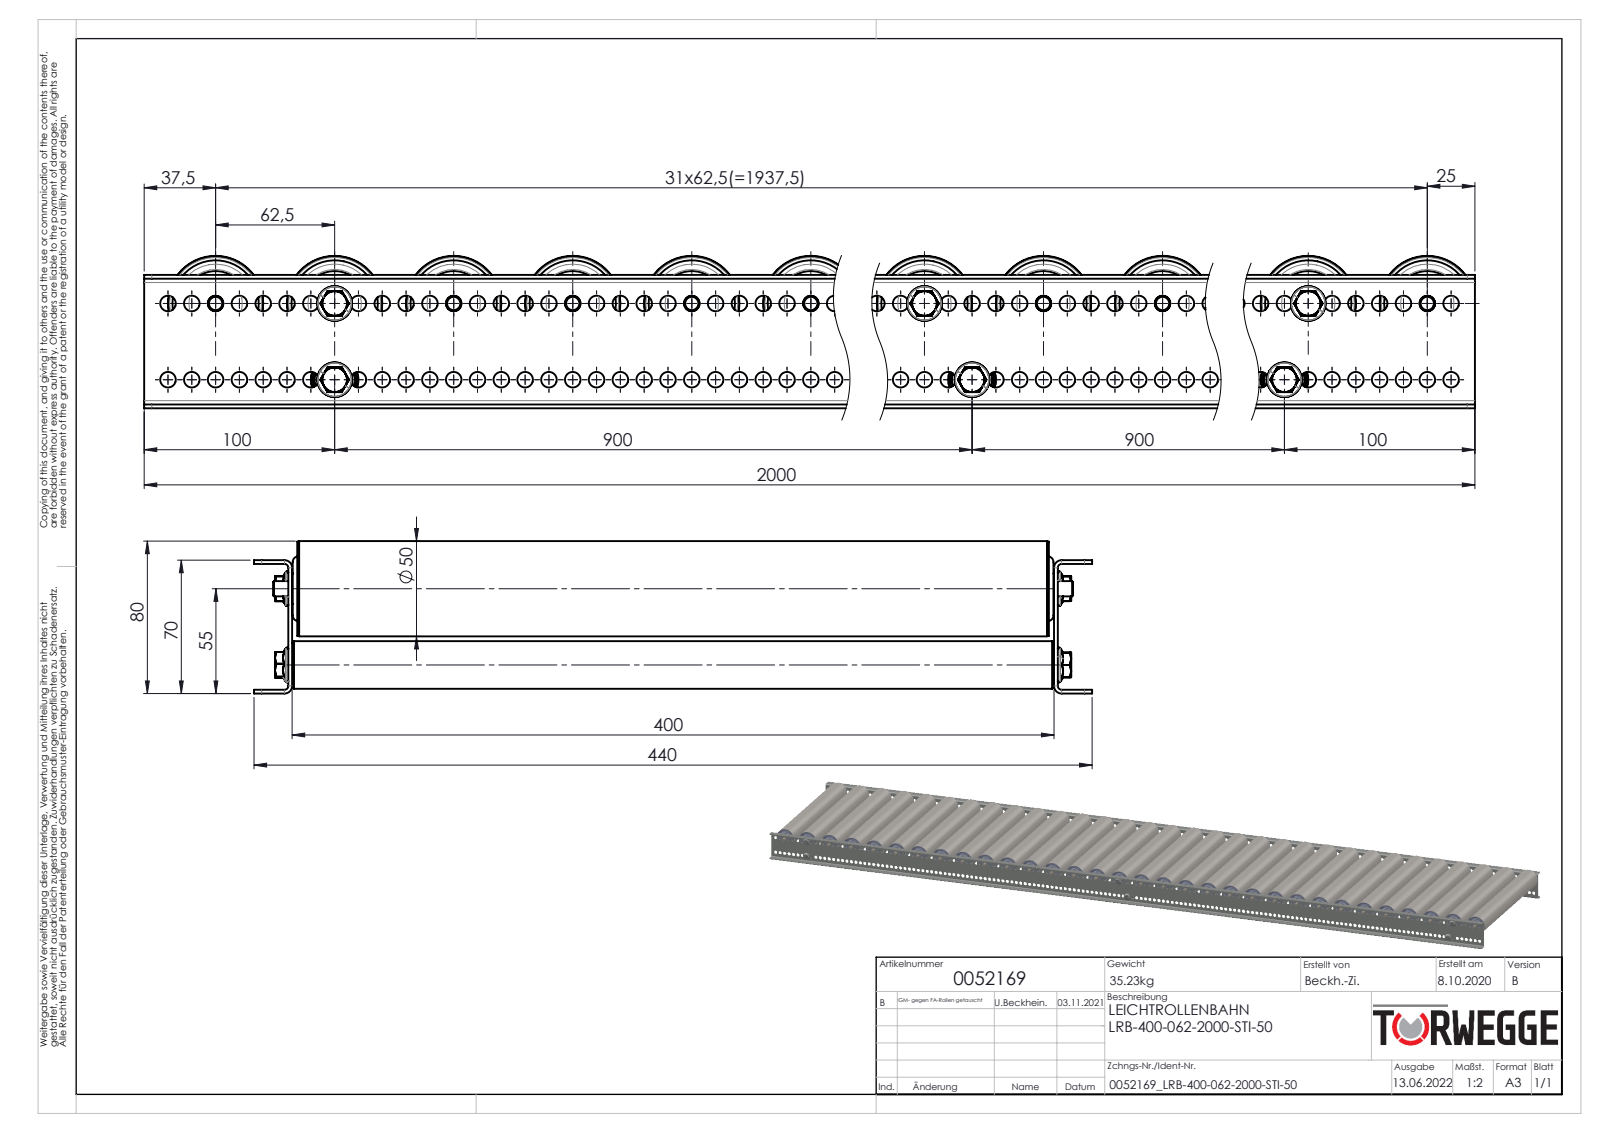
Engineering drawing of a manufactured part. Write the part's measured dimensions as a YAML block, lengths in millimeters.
part_name: "TRG-50x1,5-STI-A8-FA_KFG_0054465_TRG-50x1,5-STI-A8-FA-EL=400; 0039780-Achse-ST-Ø12-KFG_IGM8-AL=400-TRG; 0024178_Passscheibe_DIN988_12x18x1; 0052169 (+8 more)"
step_written_by: "SolidWorks 2020 (AUTOMOTIVE_DESIGN)"
units: millimeters
bodies: {solids: 728, faces: 12550, planar: 2508, cylindrical: 4480, other: 5562}
overall_size: [2000, 440, 80]
volume: 5157000
surface_area: 6111000
round_holes:
  - {diameter: 8.2, count: 318}
  - {diameter: 17.1, count: 32}
  - {diameter: 18.5, count: 32}
  - {diameter: 27.7, count: 32}
  - {diameter: 45.3, count: 32}
  - {diameter: 47, count: 32}
  - {diameter: 7.6, count: 29}
  - {diameter: 6.8, count: 6}
  - {diameter: 12, count: 3}
  - {diameter: 12.2, count: 3}
  - {diameter: 19.2, count: 3}
  - {diameter: 21, count: 3}
round_bosses_or_shafts:
  - {diameter: 8, count: 35}
  - {diameter: 50, count: 32}
  - {diameter: 49.5, count: 32}
  - {diameter: 47.3, count: 32}
  - {diameter: 29.7, count: 32}
  - {diameter: 27.4, count: 32}
  - {diameter: 27.3, count: 32}
  - {diameter: 16, count: 32}
partial_cylinders:
  - {radius: 0.6, count: 58}
  - {radius: 0.75, count: 58}
  - {radius: 2.45, count: 58}
  - {radius: 4.87, count: 29}
  - {radius: 7, count: 29}
  - {radius: 2.5, count: 12}
  - {radius: 4, count: 8}
  - {radius: 2, count: 4}
face_to_face_distances: [2, 402, 68, 400, 404, 70, 66, 1, 2.3, 401.7]
hole_center_spacings: [12.5, 25, 37.5, 50, 62.5, 75, 87.5, 100]
